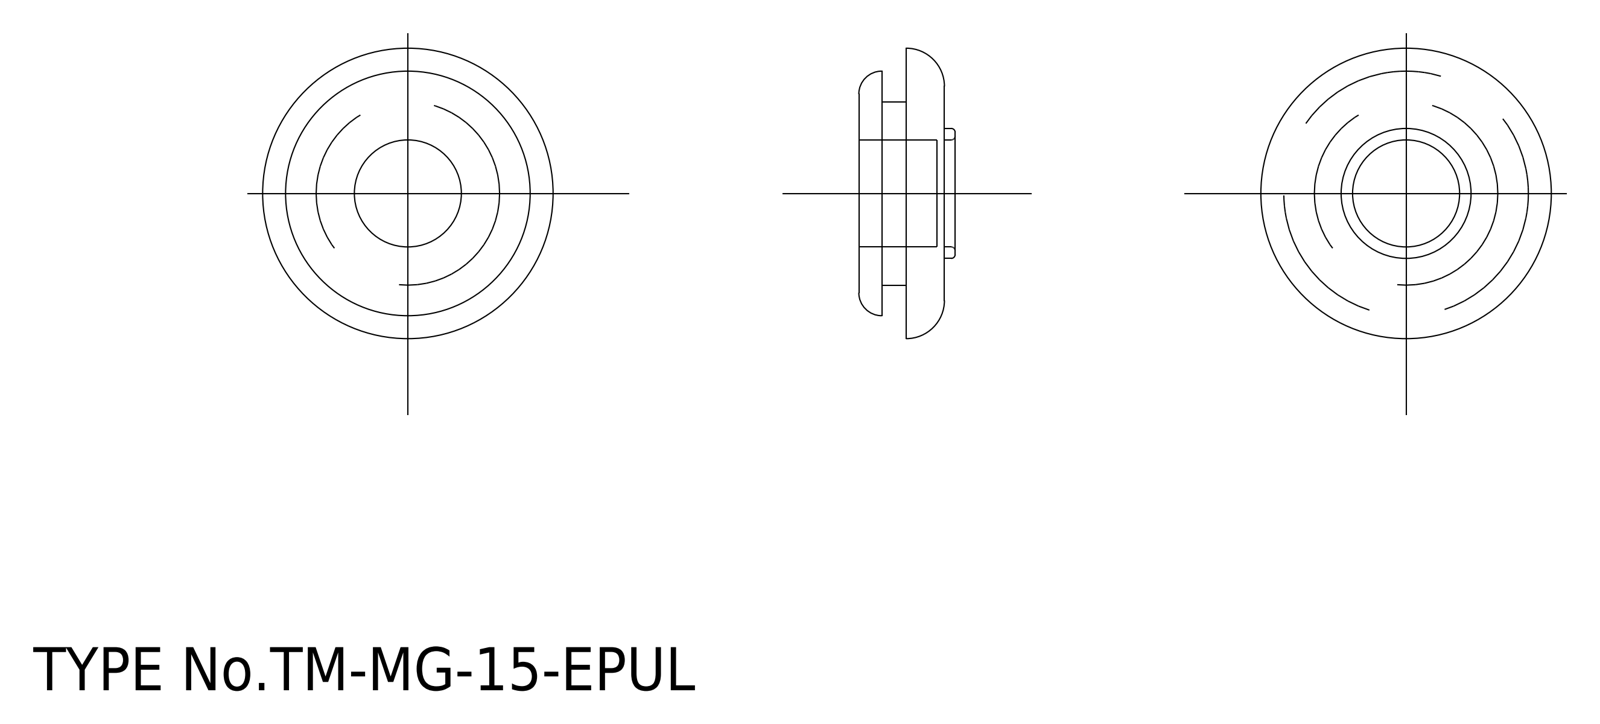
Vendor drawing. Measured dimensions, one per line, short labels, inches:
written by: spGate 15.6.1 (AUTOMOTIVE_DESIGN)
unit: in
bodies: 1 solid, 23 faces (7 planar, 8 cylindrical, 8 other)
size: 0.748 × 0.748 × 0.236
volume: 0.055 in³; area: 1.635 in²
holes: 1× ⌀0.276
bosses: 1× ⌀0.472, 1× ⌀0.335
face distances: 0.098, 0.122, 0.22, 0.059, 0.063, 0.161, 0.201, 0.142, 0.079, 0.02
